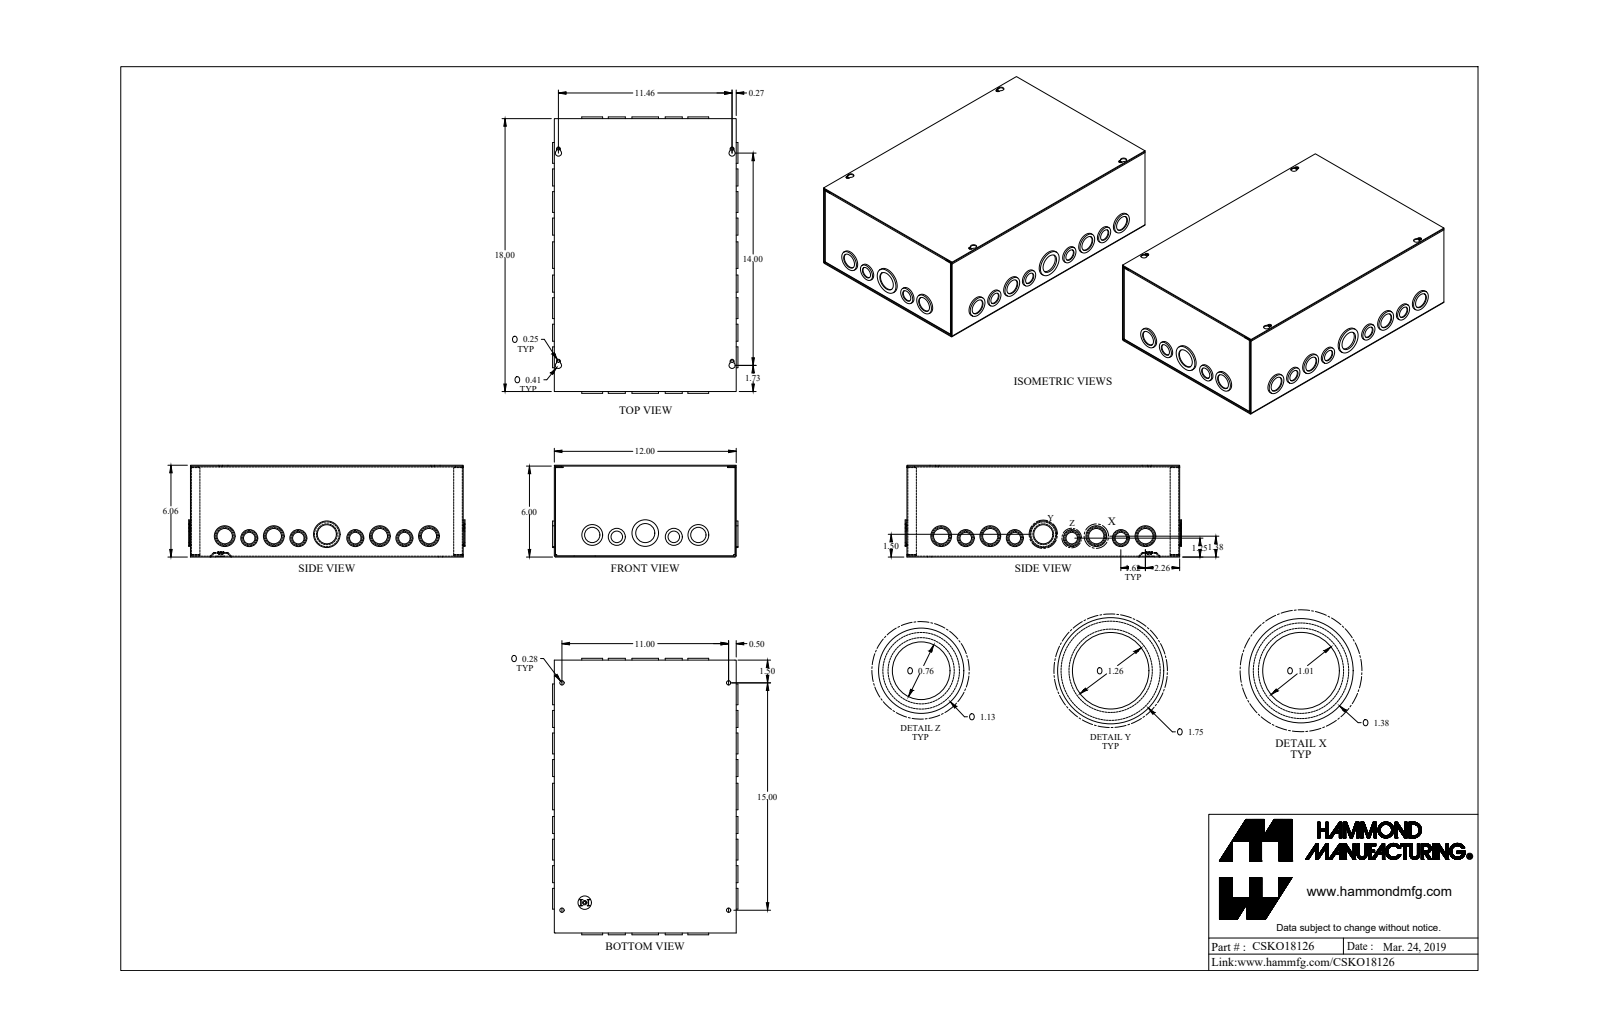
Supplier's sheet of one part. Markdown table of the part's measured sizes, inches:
| quantity | value |
| --- | --- |
| part name | CSKO18126_Default |
| STEP written by | SolidWorks 2019 (CONFIG_CONTROL_DESIGN) |
| units | inches |
| bodies | 4 solids, 541 faces (237 planar, 296 cylindrical, 8 other) |
| overall size | 18.234 × 12.234 × 6.057 |
| volume | 48.6 in³ |
| surface area | 1 719 in² |
| round holes (diameter × count) | 1.011 × 12, 1.261 × 8, 0.761 × 6, 0.17 × 5, 0.281 × 4, 1.636 × 2, 0.5 × 1 |
| round bosses / shafts (diameter × count) | 1.125 × 10, 1.375 × 7, 0.875 × 6, 0.875 × 4, 1.375 × 3, 1.75 × 2, 1.125 × 2, 0.492 × 1 |
| partial cylindrical surfaces (radius × count) | 0.029 × 12, 0.086 × 12, 0.057 × 8, 0.125 × 4, 0.203 × 4 |
| main face-to-face distances | 0.057, 6, 5.943, 6.057, 11.943, 17.943, 12, 11.886, 18, 17.886 |
| hole center spacings | 1.625, 0.55, 1.896, 3.24, 3.502, 5.381, 7, 8.621 |
